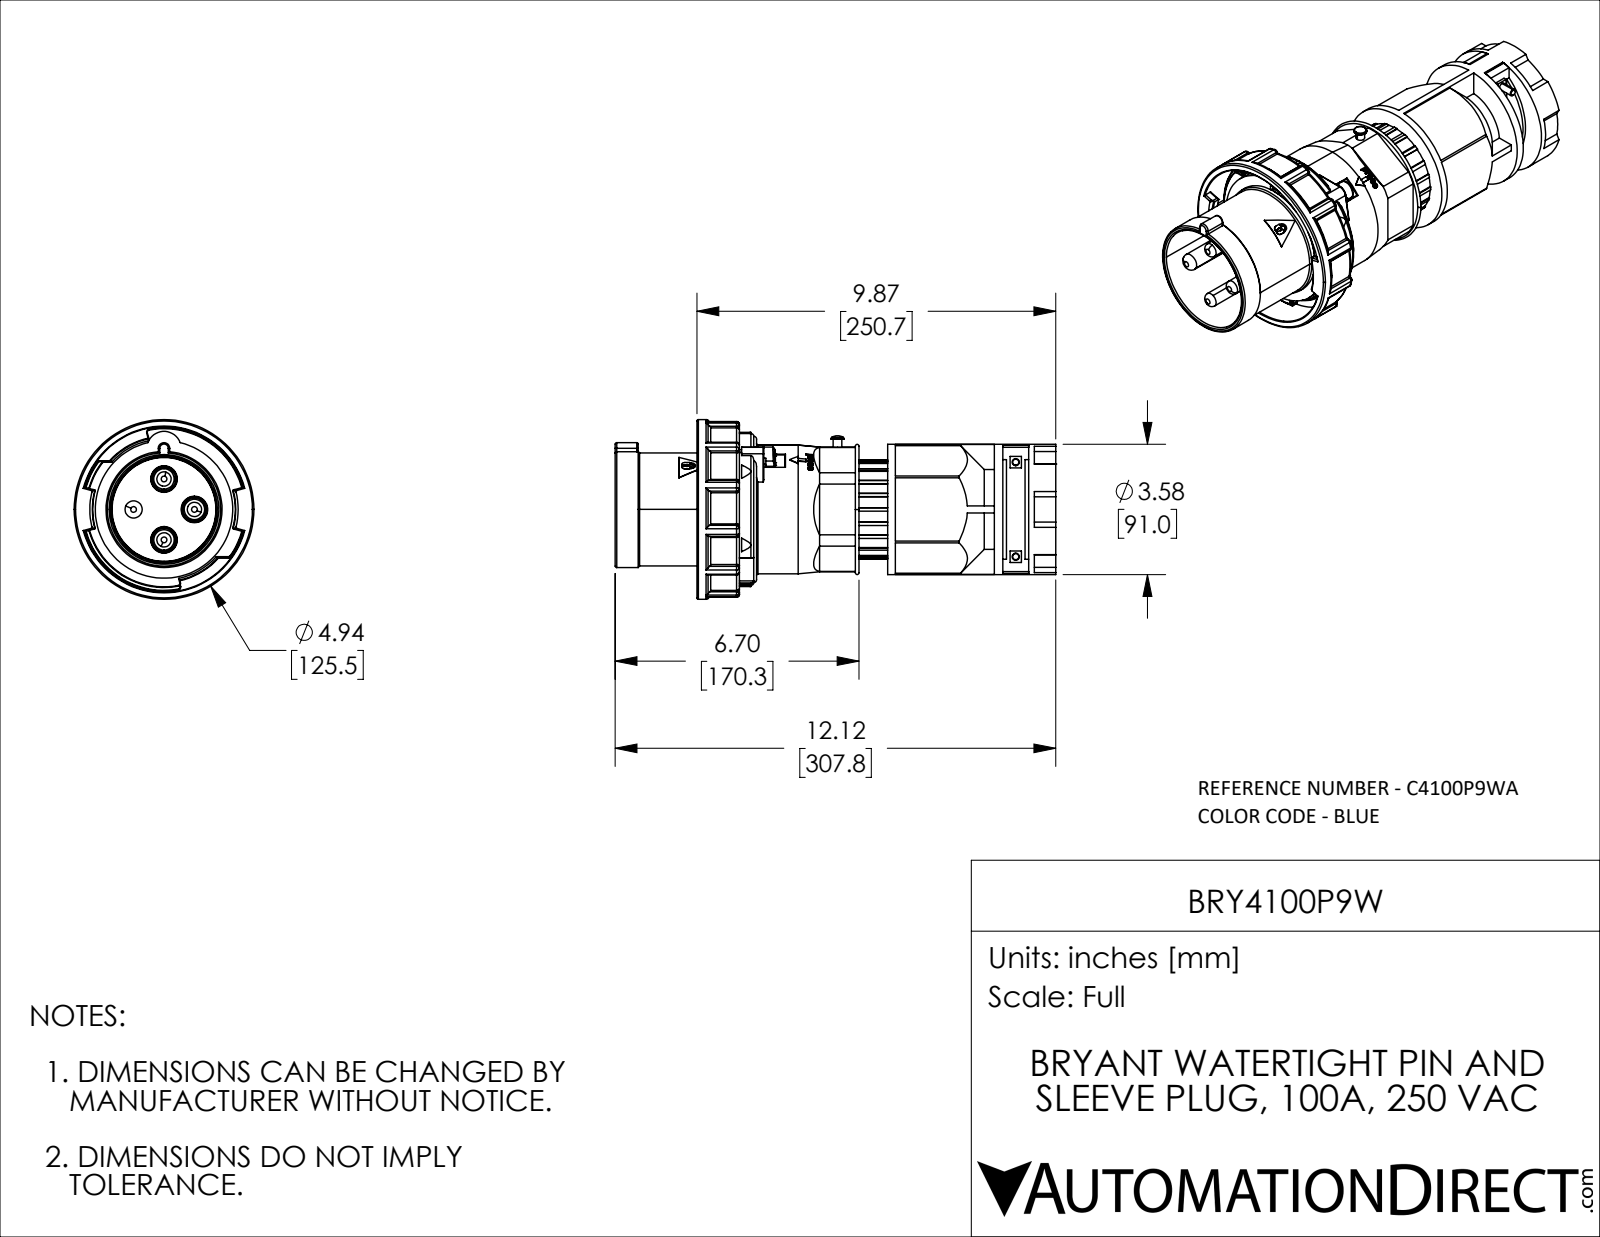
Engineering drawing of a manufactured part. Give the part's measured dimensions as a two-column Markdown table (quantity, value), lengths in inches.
| quantity | value |
| --- | --- |
| part name | BRY4100P9W |
| STEP written by | SolidWorks 2021 (CONFIG_CONTROL_DESIGN) |
| units | inches |
| bodies | 6 solids, 1386 faces (405 planar, 470 cylindrical, 511 other) |
| overall size | 12.116 × 4.941 × 4.941 |
| volume | 69.99 in³ |
| surface area | 338.8 in² |
| round holes (diameter × count) | 1.969 × 1, 3.189 × 1, 4.547 × 1 |
| round bosses / shafts (diameter × count) | 0.394 × 3, 0.197 × 2, 4.941 × 1, 3.78 × 1, 3.583 × 1, 3.543 × 1, 3.193 × 1, 3.11 × 1 |
| partial cylindrical surfaces (radius × count) | 0.079 × 56, 0.039 × 42, 0.02 × 30, 0.098 × 6, 0.047 × 2, 0.069 × 2, 0.157 × 2, 0.236 × 2 |
| main face-to-face distances | 3.13, 4.665, 0.709, 3.957, 0.945, 1.063, 0.098, 1.286, 1.844, 3.72 |
